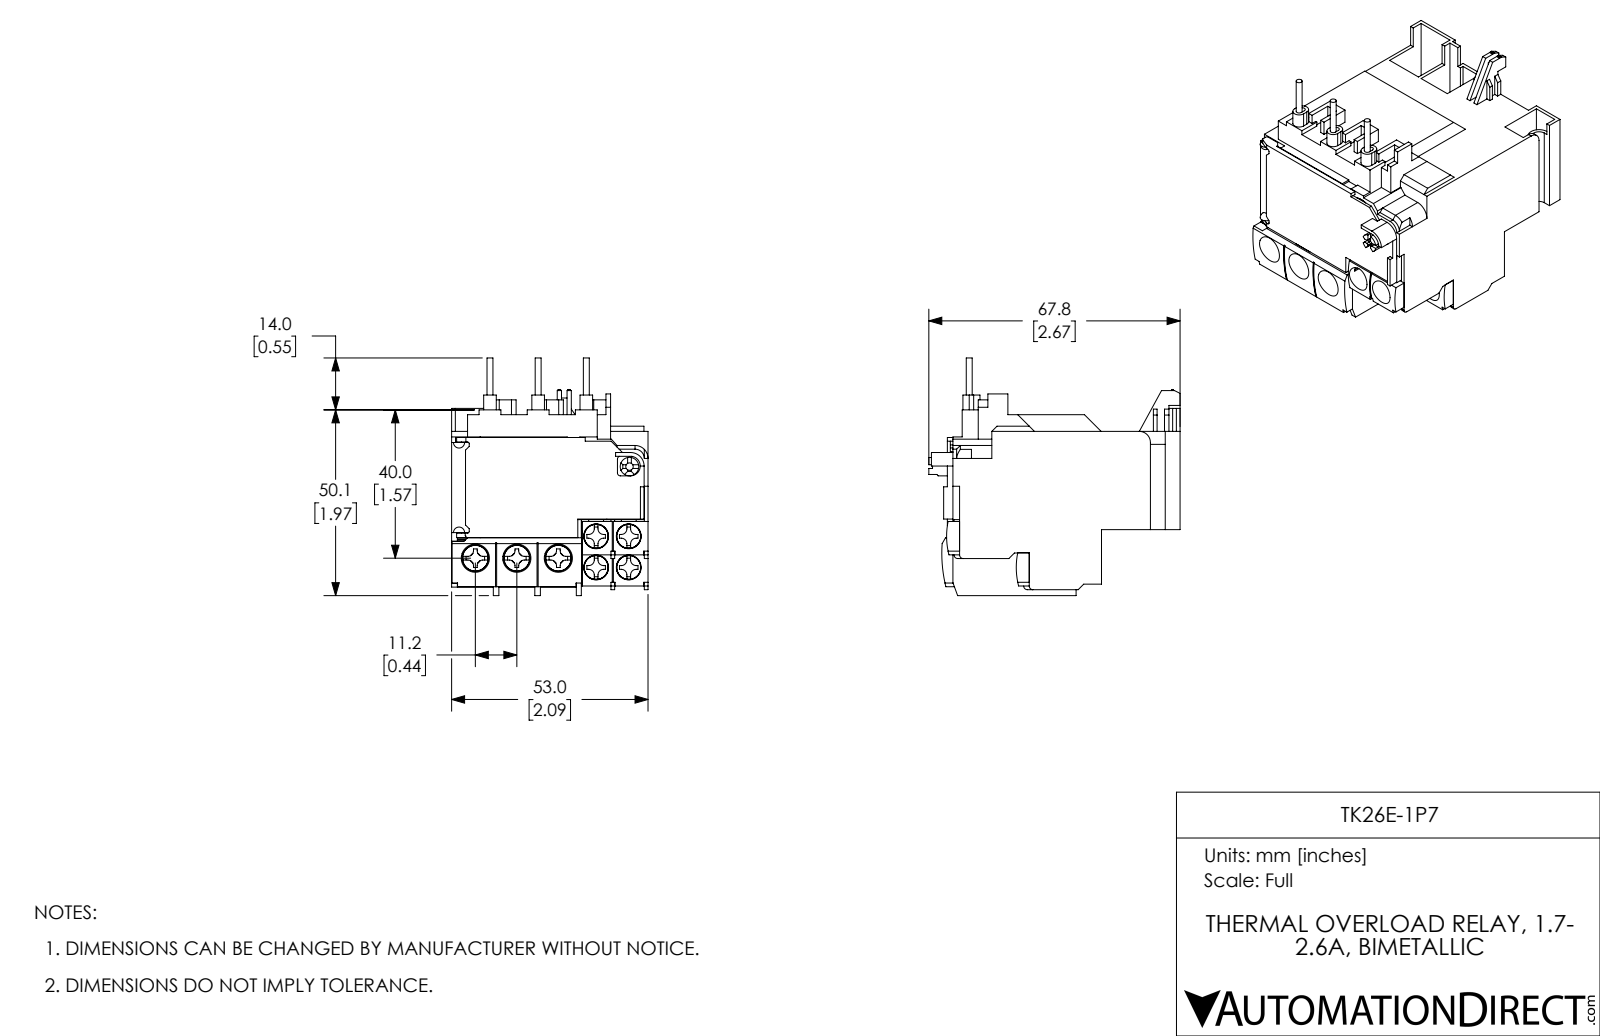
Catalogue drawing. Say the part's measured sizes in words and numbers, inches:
The part is named "TK26E-1P7". Its 3-D file was written by "SolidWorks 2017 (AUTOMOTIVE_DESIGN)". It is 38 solids with 1480 faces: 1225 planar, 220 cylindrical and 35 other. Overall it measures 2.669 by 2.524 by 2.087 inches. Its volume is 6.099 cubic inches and its surface area 60.15 square inches. Round holes: 4 of diameter 0.138, 4 of diameter 0.142, 4 of diameter 0.264, 3 of diameter 0.157, 3 of diameter 0.161, 3 of diameter 0.299, 1 of diameter 0.039, 1 of diameter 0.079, 1 of diameter 0.197, 1 of diameter 0.433. Round bosses or shafts: 4 of diameter 0.26, 3 of diameter 0.063, 1 of diameter 0.236. Partial cylindrical surfaces (rounded edges, fillets, slot ends): 28 of radius 0.059, 8 of radius 0.039, 6 of radius 0.02, 6 of radius 0.067, 5 of radius 0.031, 4 of radius 0.047, 4 of radius 0.171, 3 of radius 0.189. The main face-to-face distances are 0.039, 0.354, 0.059, 0.472, 2.087, 0.079, 0.394, 0.433, 0.343, 0.028. The hole center spacings are 0.331, 0.346, 0.441, 0.479, 0.376, 0.413, 0.464, 0.74.
